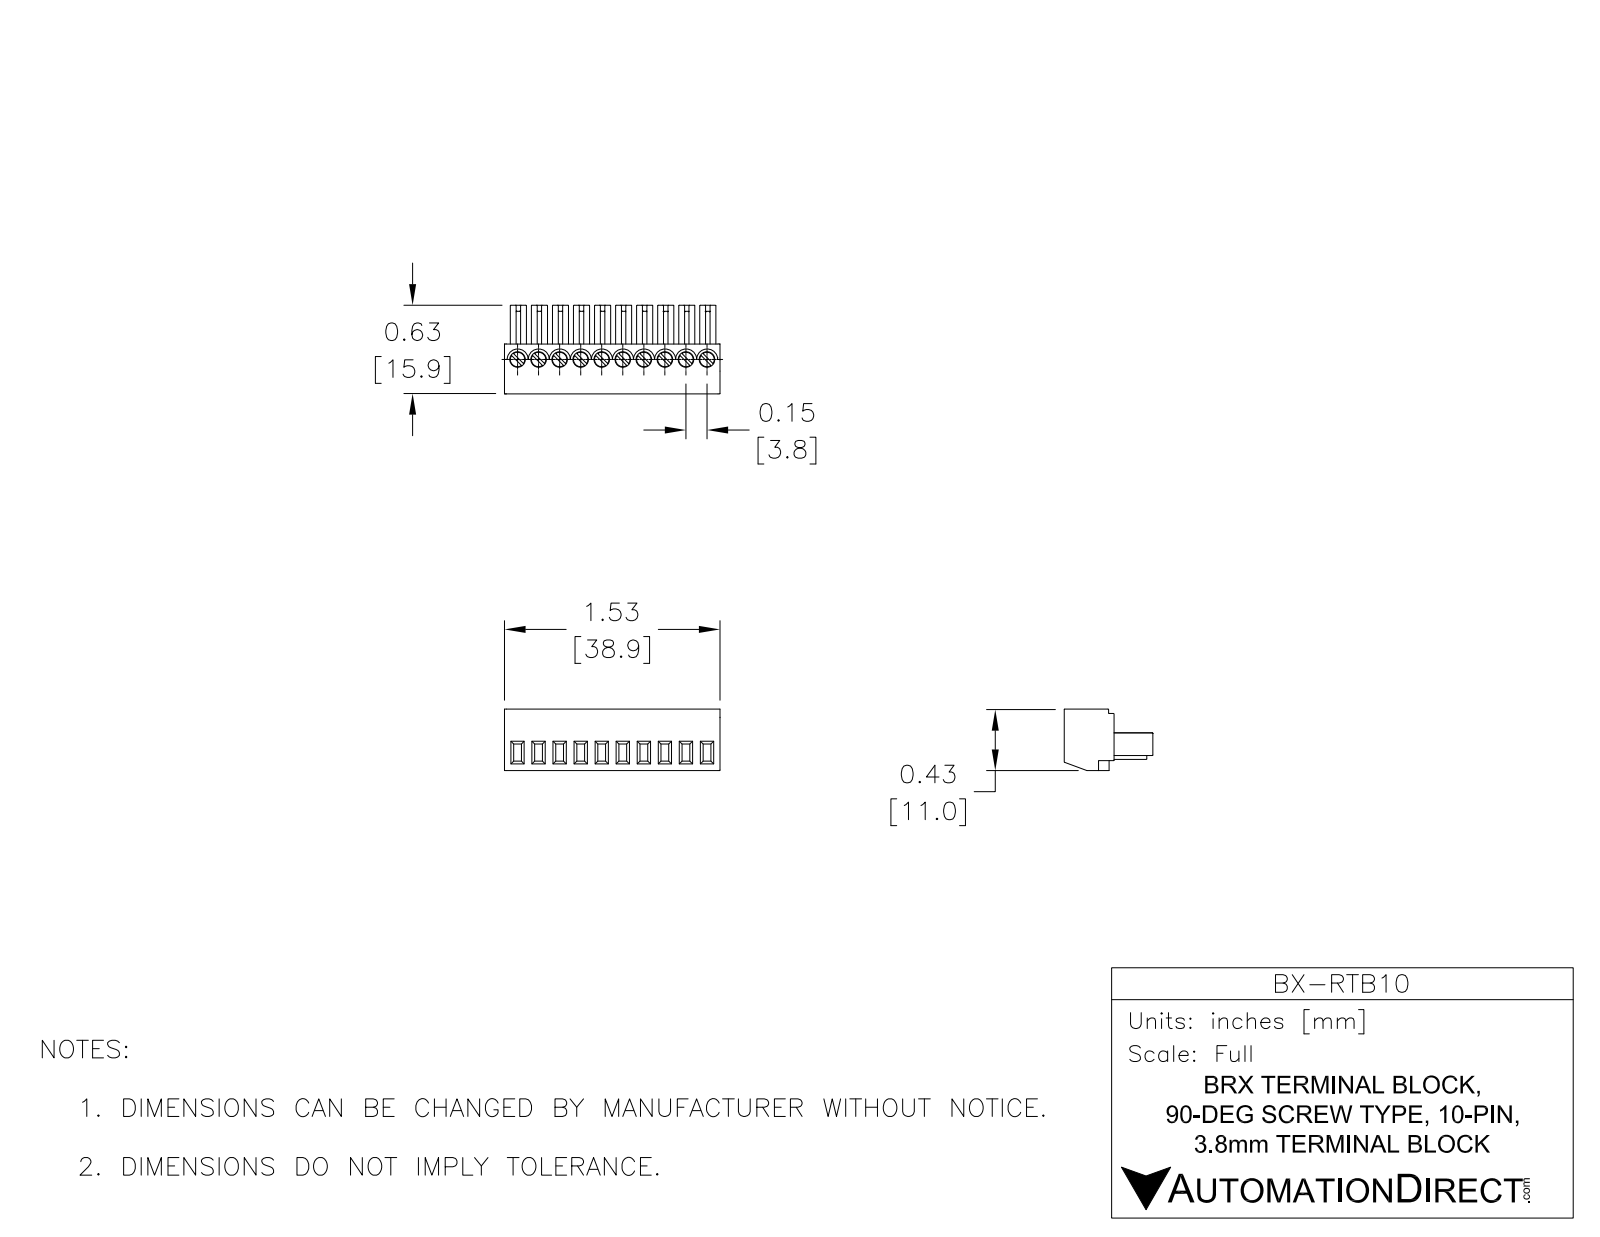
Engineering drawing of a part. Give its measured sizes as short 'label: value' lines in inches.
name: BX-RTB10
written by: SolidWorks 2016 (AUTOMOTIVE_DESIGN)
unit: in
bodies: 0 solids, 836 faces (321 planar, 381 cylindrical, 134 other)
size: 1.531 × 0.63 × 0.437
holes: 10× ⌀0.039, 10× ⌀0.079, 10× ⌀0.11
bosses: 10× ⌀0.102
rounds: 153× R0.004, 20× R0.012, 10× R0.072, 10× R0.075, 2× R0.02
face distances: 0.15, 0.299, 0.449, 0.598, 0.354, 0.748, 0.115, 0.414, 0.264, 0.035
hole spacings: 0.15, 0.299, 0.449, 0.598, 0.748, 0.898, 1.047, 1.197
